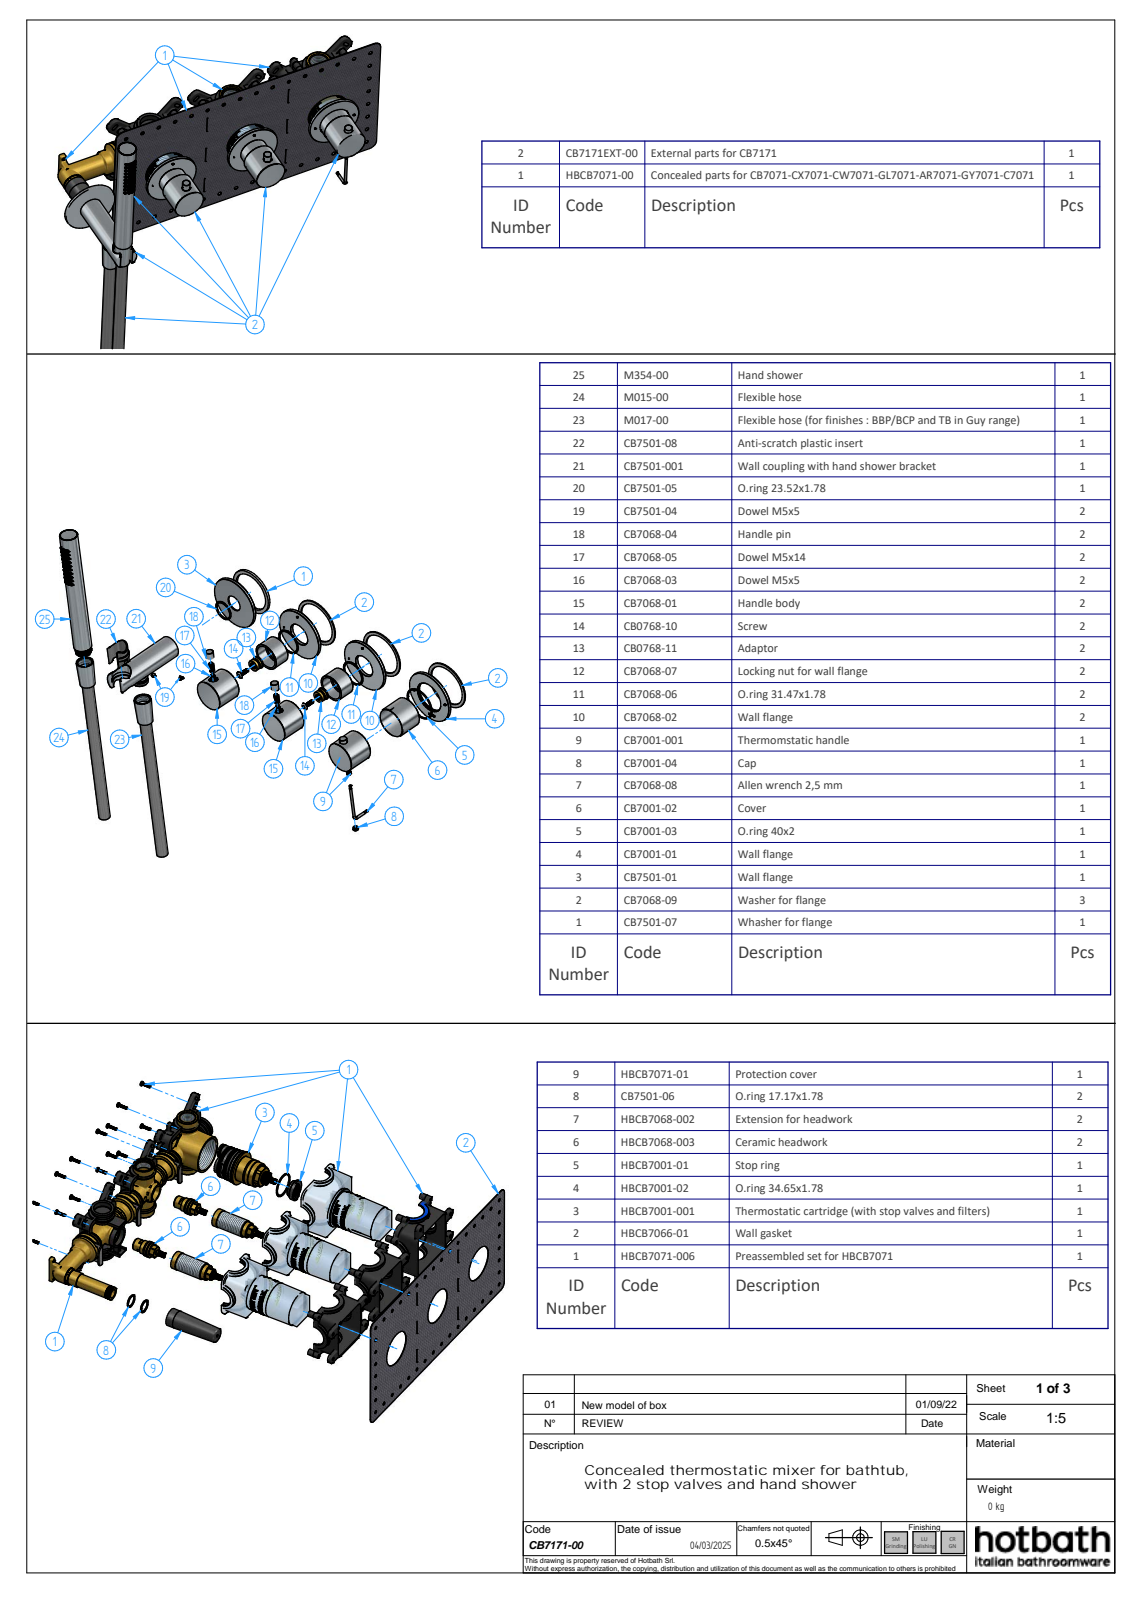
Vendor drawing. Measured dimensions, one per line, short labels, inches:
name: CB7171EXT-00; CB7501-04; CB7501-01; M015-001 (+8 more)
written by: Solid Edge (AUTOMOTIVE_DESIGN)
unit: in
bodies: 24 solids, 1448 faces (456 planar, 380 cylindrical, 612 other)
size: 18.322 × 14.007 × 13.614
volume: 15.97 in³; area: 277.7 in²
holes: 41× ⌀0.126, 5× ⌀0.163, 4× ⌀0.118, 4× ⌀0.138, 3× ⌀0.205, 3× ⌀2.638, 2× ⌀0.177, 2× ⌀0.402, 2× ⌀0.598, 2× ⌀0.65, 2× ⌀0.733, 2× ⌀0.866
bosses: 4× ⌀2.835, 3× ⌀2.244, 3× ⌀0.394, 2× ⌀1.457, 2× ⌀0.591, 2× ⌀0.295, 2× ⌀0.197, 1× ⌀2.047
rounds: 22× R0.008, 15× R0.02, 6× R0.012, 4× R0.014, 4× R0.138, 3× R0.023, 3× R0.03, 2× R0.009
face distances: 0.157, 0.156, 0.159, 0.118, 0.039, 0.159, 0.161, 0.154, 0.12, 0.037
hole spacings: 0.498, 0.236, 0.284, 0.726, 0.472, 0.709, 0.958, 0.394
